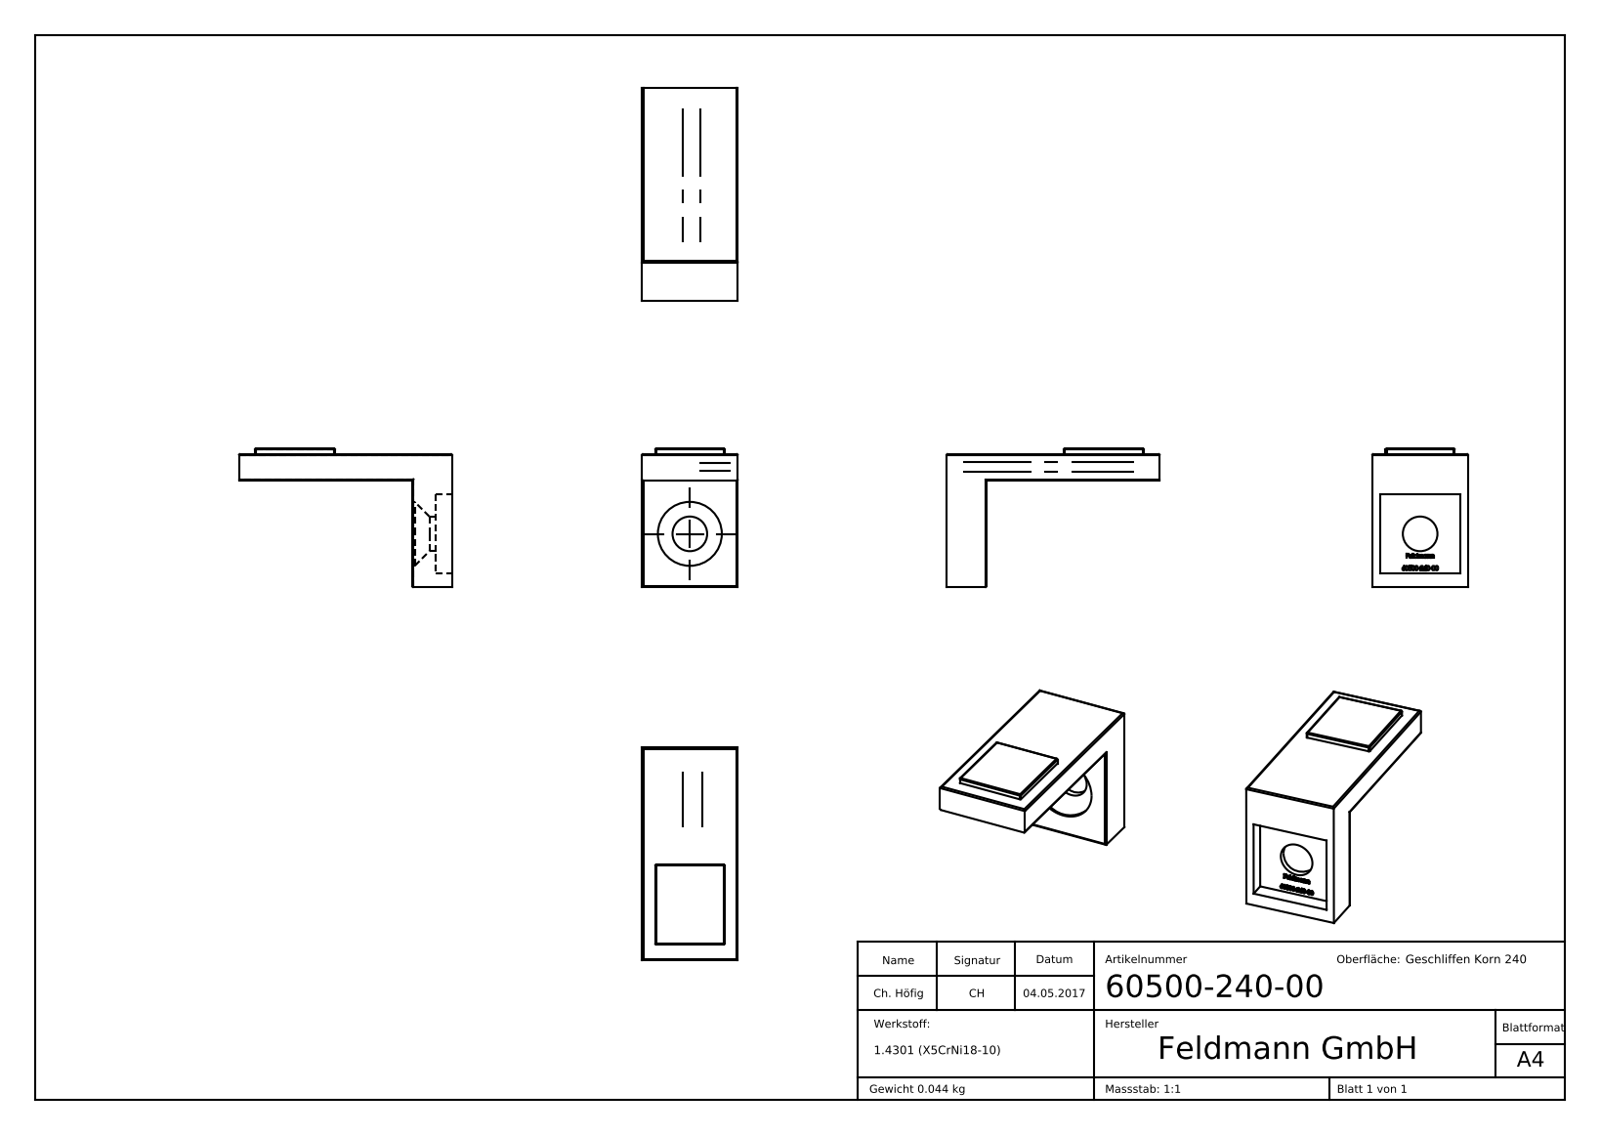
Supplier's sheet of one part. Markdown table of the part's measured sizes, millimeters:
| quantity | value |
| --- | --- |
| part name | 60500-240-00 |
| STEP written by | SolidWorks 2015 (CONFIG_CONTROL_DESIGN) |
| units | millimeters |
| bodies | 2 solids, 292 faces (140 planar, 21 cylindrical, 131 other) |
| overall size | 40 × 26 × 18 |
| volume | 5 528 mm³ |
| surface area | 3 653 mm² |
| round holes (diameter × count) | 6.5 × 1, 12 × 1 |
| partial cylindrical surfaces (radius × count) | 0.25 × 9, 0.2 × 8 |
| main face-to-face distances | 5, 18, 7.5, 1, 3, 4.5, 6, 20, 25, 26 |
